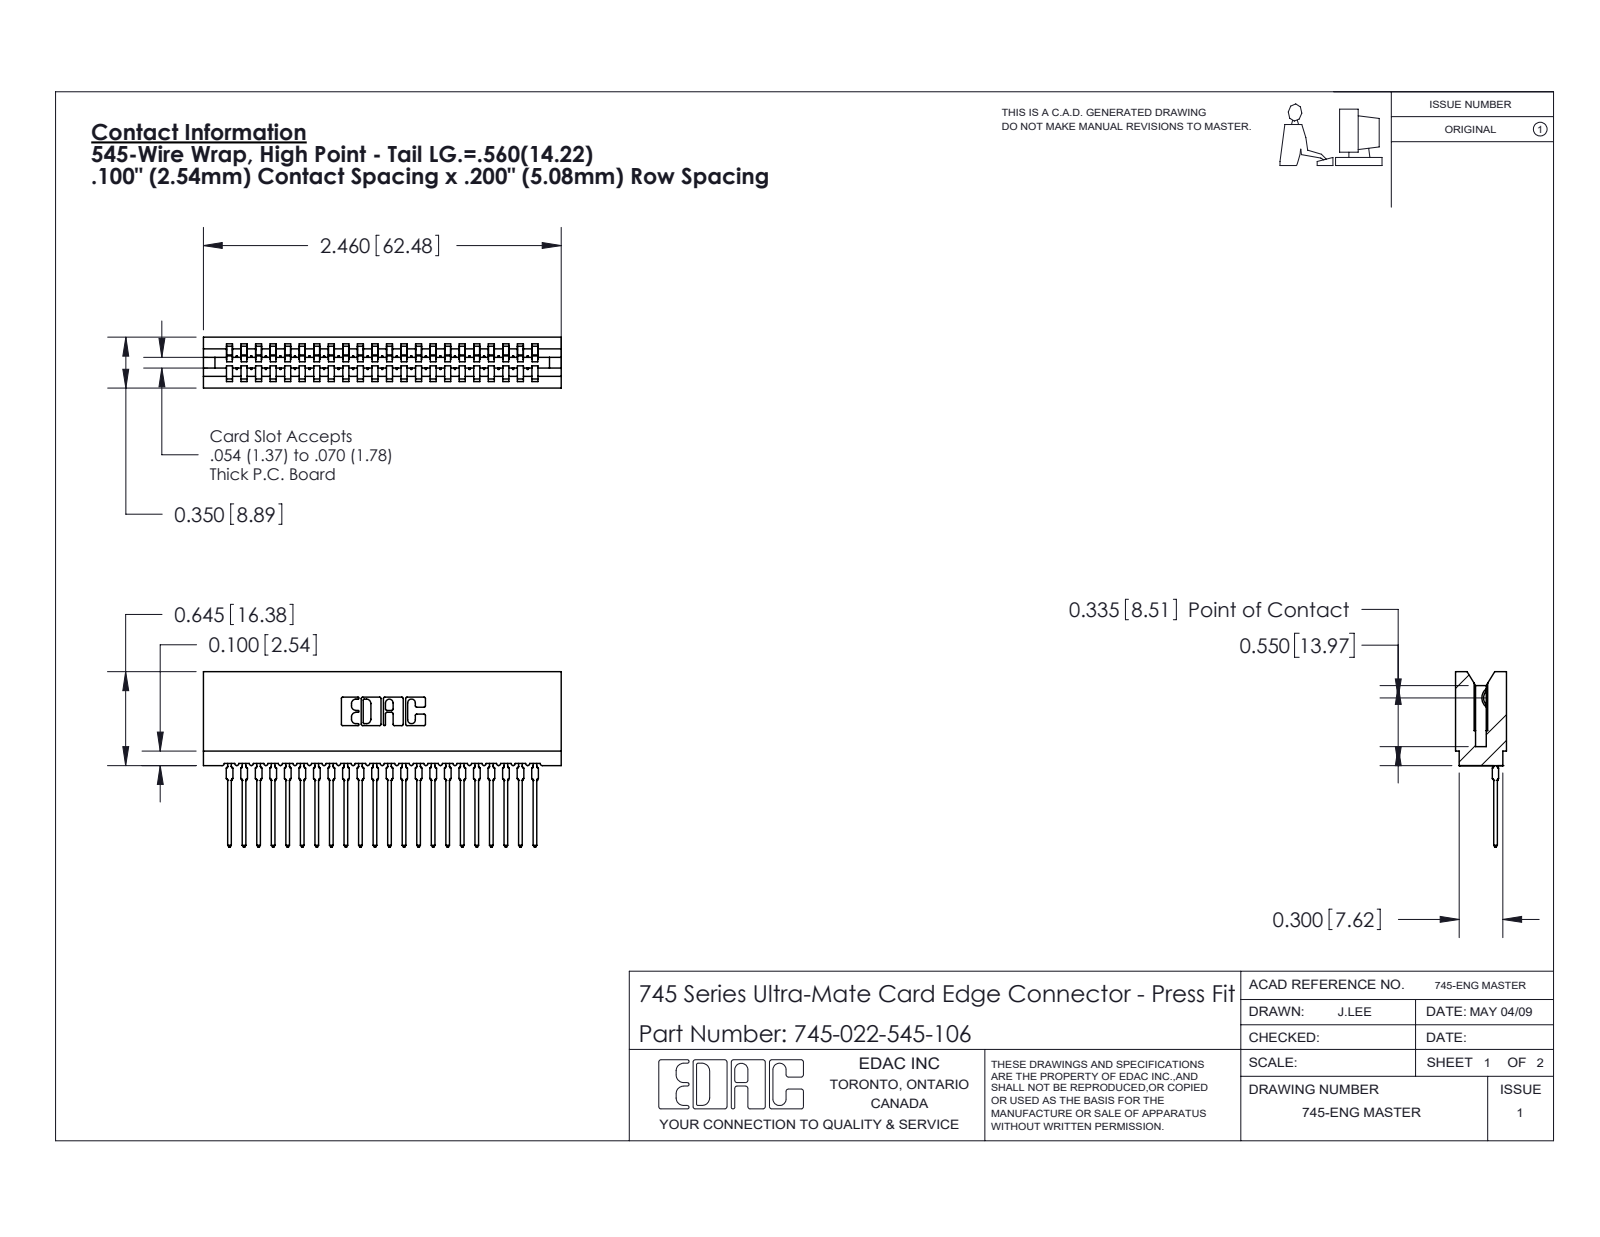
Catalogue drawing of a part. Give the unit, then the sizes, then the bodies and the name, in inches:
Units: inches
Overall size (bounding box): 2.46 × 1.206 × 0.35
Partial cylindrical surfaces — rounded edges, fillets, slot ends (radius × count): R0.015 ×44, R0.021 ×44, R0.01 ×22, R0.007 ×6, R0.031 ×6, R0.005 ×4, R0.011 ×4, R0.026 ×3
Main face-to-face distances: 0.2, 0.1, 0.3, 0.4, 0.35, 0.5, 0.6, 0.138, 0.212, 0.7
Volume: 0.341 in³ · Surface area: 16.07 in²
Bodies: 23 solids, 2560 faces (1530 planar, 458 cylindrical, 572 other)
Part name (STEP PRODUCT): 745-022-545-106; 745-292-001_545; 745 Part_Insulator Option - 06
STEP written by: SolidWorks 2020 (CONFIG_CONTROL_DESIGN)
